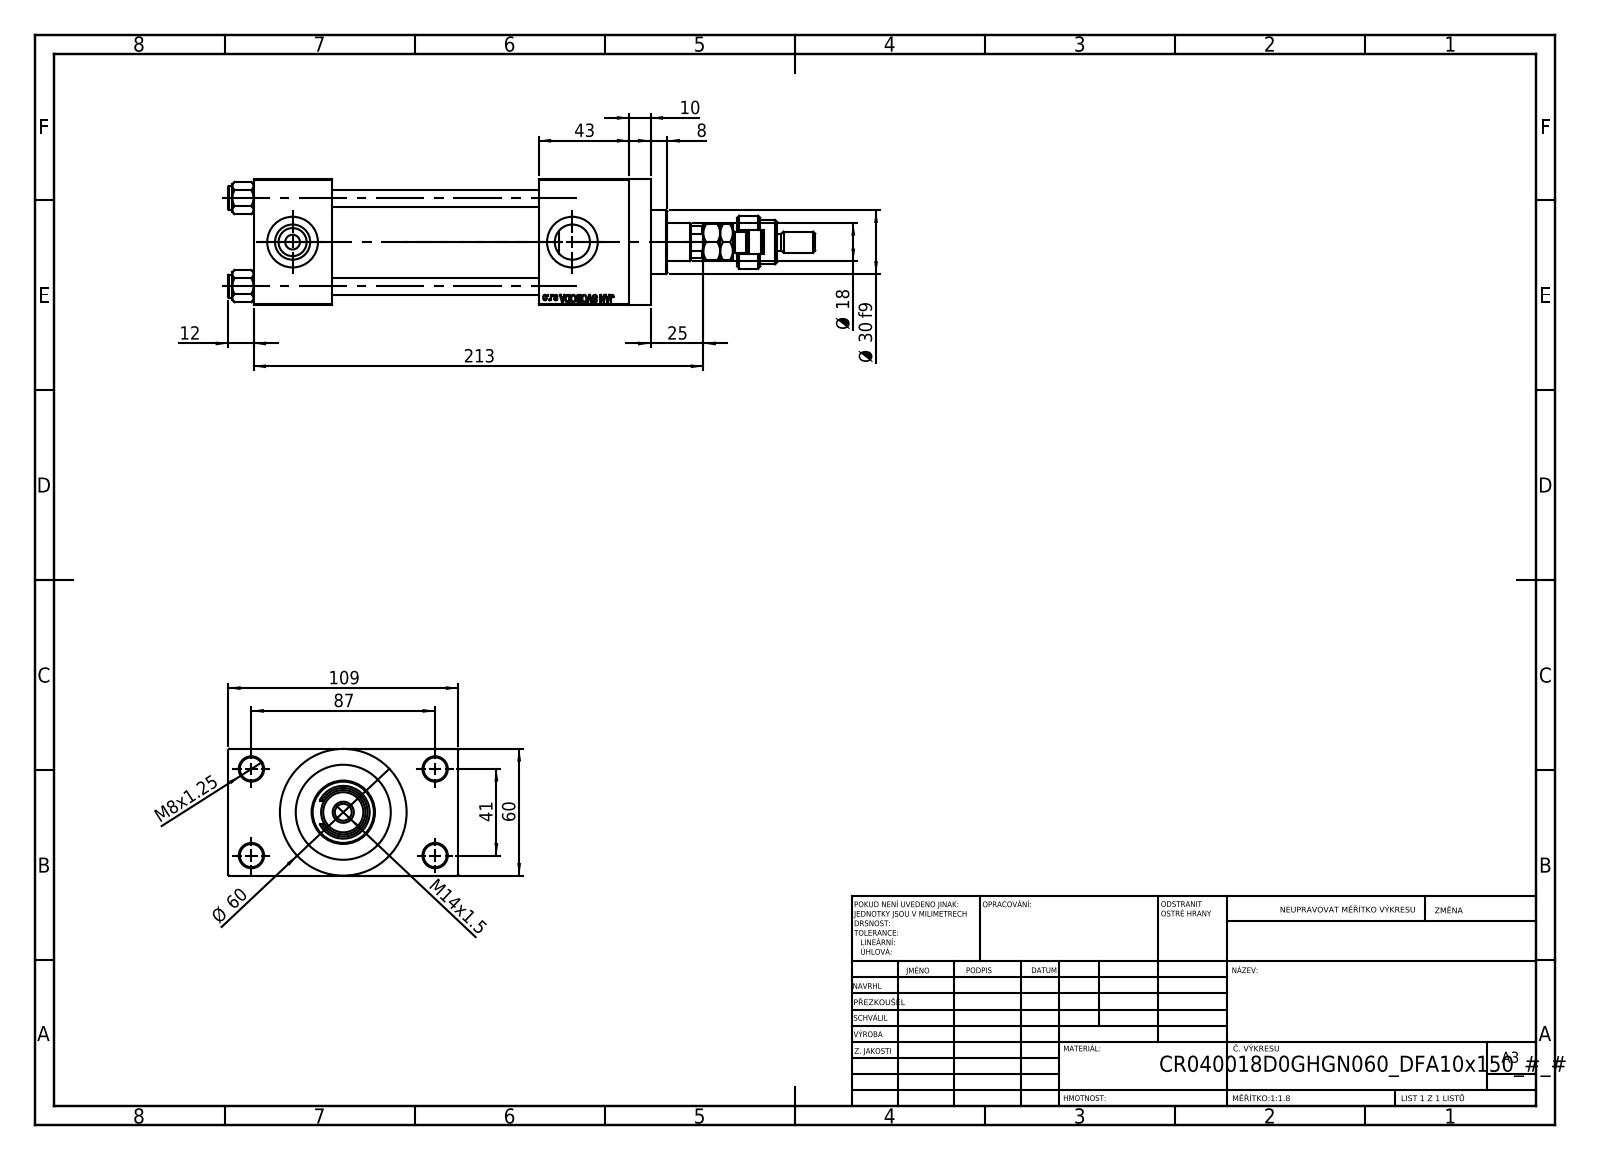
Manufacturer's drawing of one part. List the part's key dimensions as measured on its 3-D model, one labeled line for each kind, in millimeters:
Part name (STEP PRODUCT): NUT_M5_D; V215CR_D_TYCINKA; MFA; V215_VC_A (+3 more)
STEP written by: SolidWorks 2019 (CONFIG_CONTROL_DESIGN)
Units: millimetres
Bodies: 13 solids, 1189 faces (526 planar, 101 cylindrical, 562 other)
Overall size (bounding box): 278 × 109 × 60
Volume: 558 749 mm³ · Surface area: 145 082 mm²
Round holes (diameter × count): ⌀8 ×4, ⌀11 ×4, ⌀7 ×2, ⌀16.66 ×2, ⌀24 ×2, ⌀8.5 ×1, ⌀18 ×1, ⌀21 ×1, ⌀31 ×1, ⌀40 ×1, ⌀45 ×1
Round bosses / shafts (diameter × count): ⌀11 ×4, ⌀60 ×1, ⌀46 ×1, ⌀30 ×1, ⌀25 ×1, ⌀16 ×1, ⌀10 ×1, ⌀8 ×1
Partial cylindrical surfaces — rounded edges, fillets, slot ends (radius × count): R5.5 ×1, R8.5 ×1, R8.75 ×1
Main face-to-face distances: 60, 98, 24.5, 84.5, 37, 135, 178, 141, 43, 53
Hole centre spacings: 22.65, 29.49, 41.7, 47.15, 48.09, 64.35, 76.49, 41
